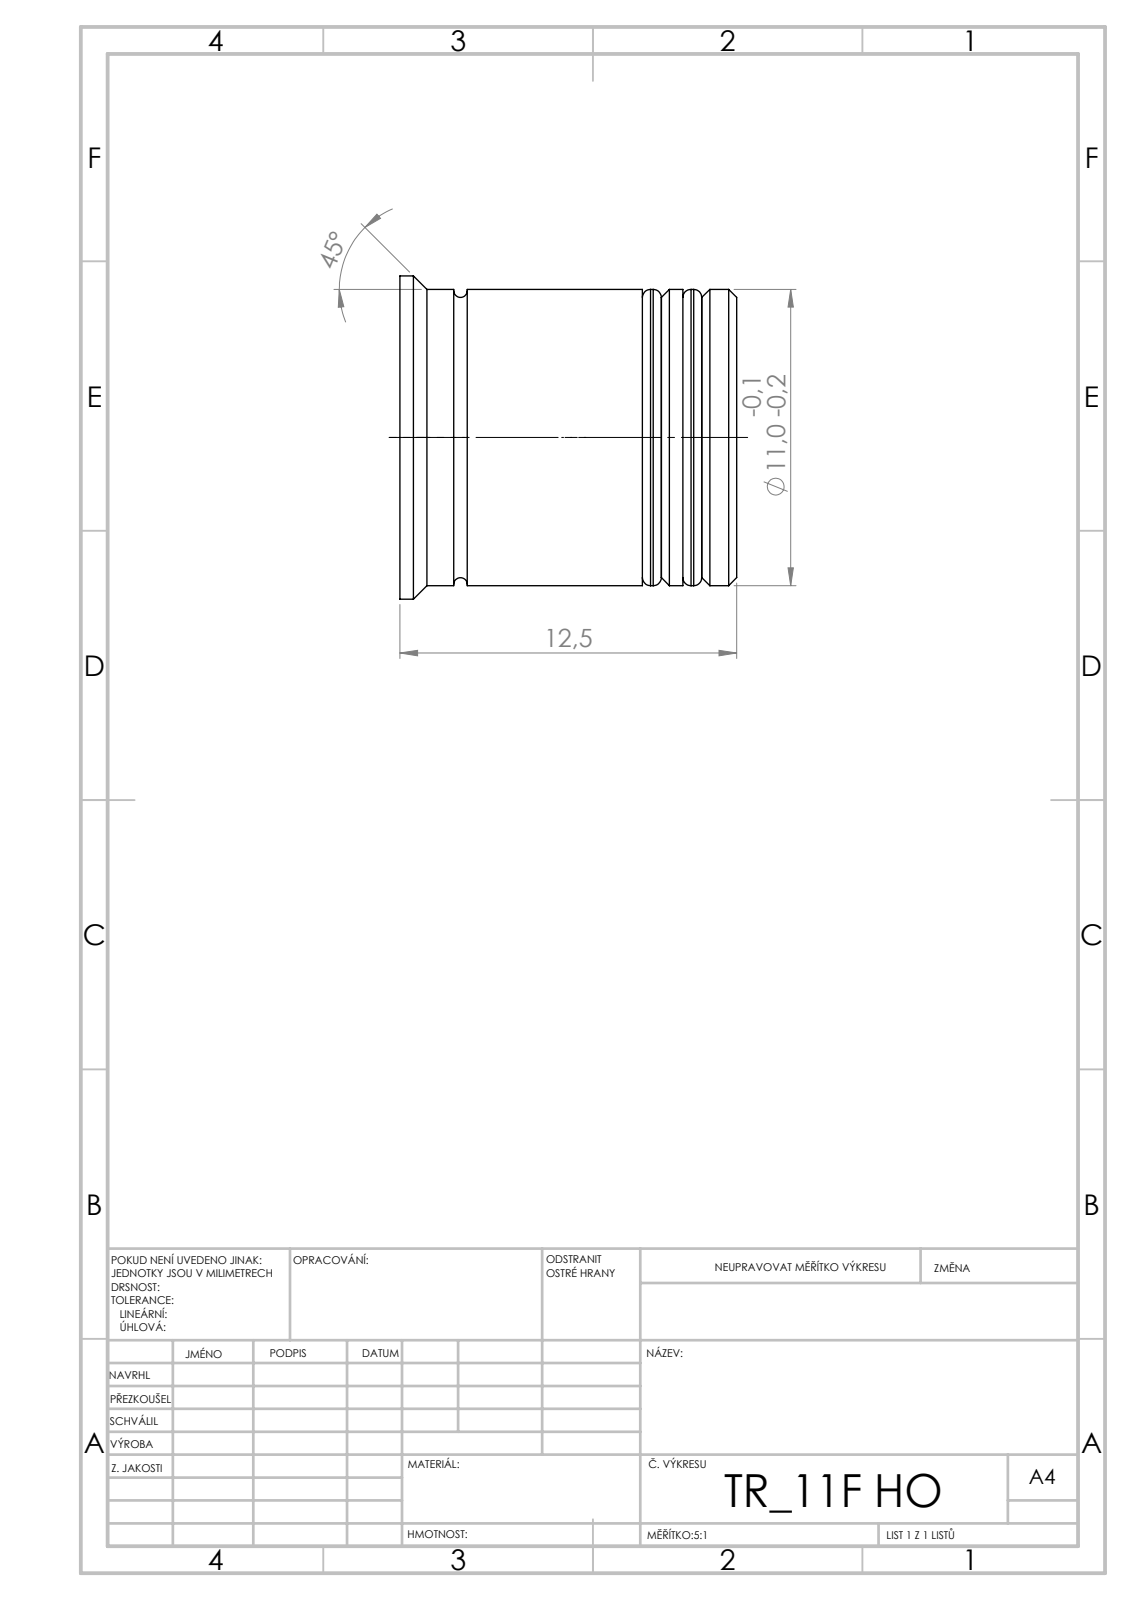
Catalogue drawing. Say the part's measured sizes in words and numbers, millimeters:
Its 3-D file was written by "SolidWorks 2019 (CONFIG_CONTROL_DESIGN)". It is 3 solids with 74 faces: 29 planar, 25 cylindrical and 20 other. Overall it measures 12.5 by 12 by 12 millimeters. Its volume is 1 247 cubic millimeters and its surface area 1 171 square millimeters. Round bosses or shafts: 1 of diameter 12, 1 of diameter 11, 1 of diameter 10.4, 1 of diameter 8. The main face-to-face distances are 1.5, 0.7, 8, 2, 2.2, 0.8, 1.3, 2.8, 3.5, 1.
